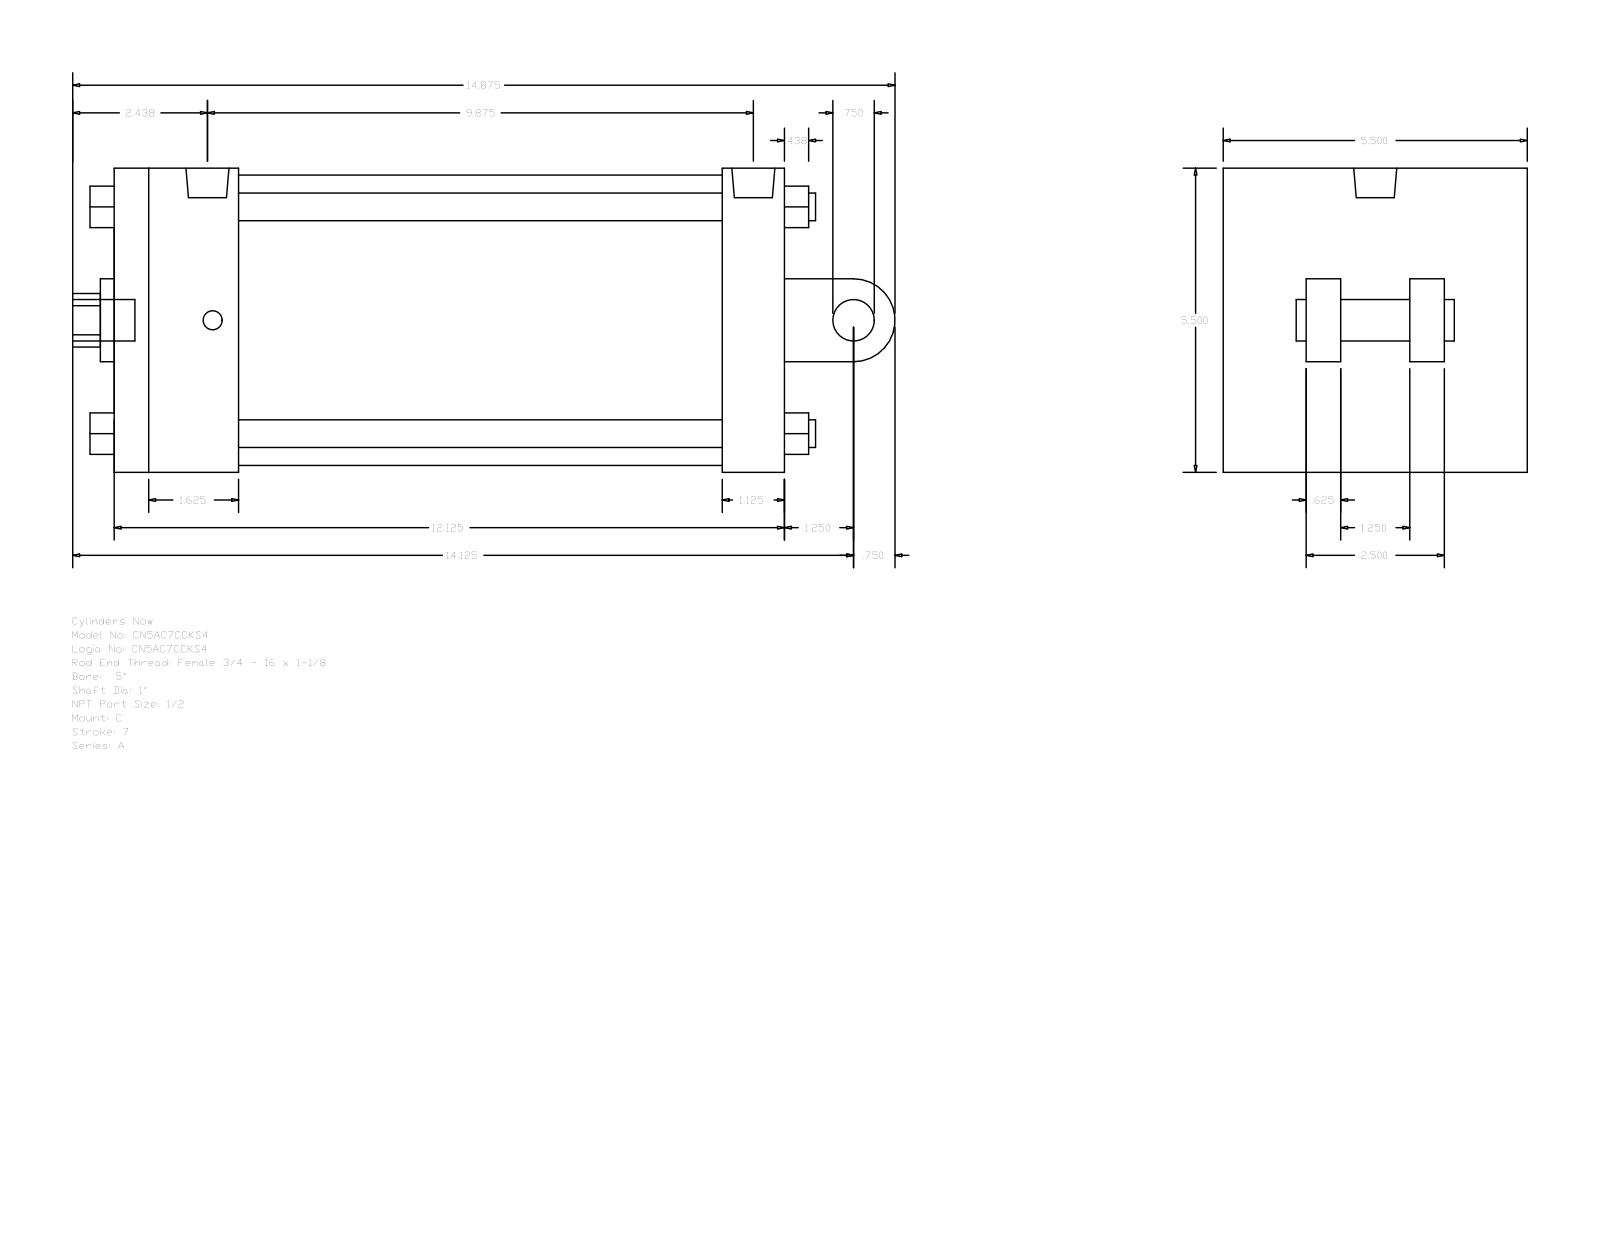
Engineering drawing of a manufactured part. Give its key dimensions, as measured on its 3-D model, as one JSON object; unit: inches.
{"part_name": "A_C__0500_1", "step_written_by": "GSSL Pune (CONFIG_CONTROL_DESIGN)", "units": "inches", "bodies": {"solids": 0, "faces": 135, "planar": 102, "cylindrical": 33, "other": 0}, "overall_size": [14.875, 5.5, 5.5], "round_holes": [[0.344, 2], [0.778, 1], [1, 1], [1.5, 1], [5.25, 1]], "round_bosses_or_shafts": [[0.5, 4], [0.75, 2], [0.344, 2], [0.778, 1]], "partial_cylinders_radius": [[0.484, 1], [0.75, 1]], "face_to_face_distances": [5.5, 12.125, 1.125, 2.25, 11, 8.75, 9.875, 1.5, 0.625, 1.875], "hole_center_spacings": [0.094]}
